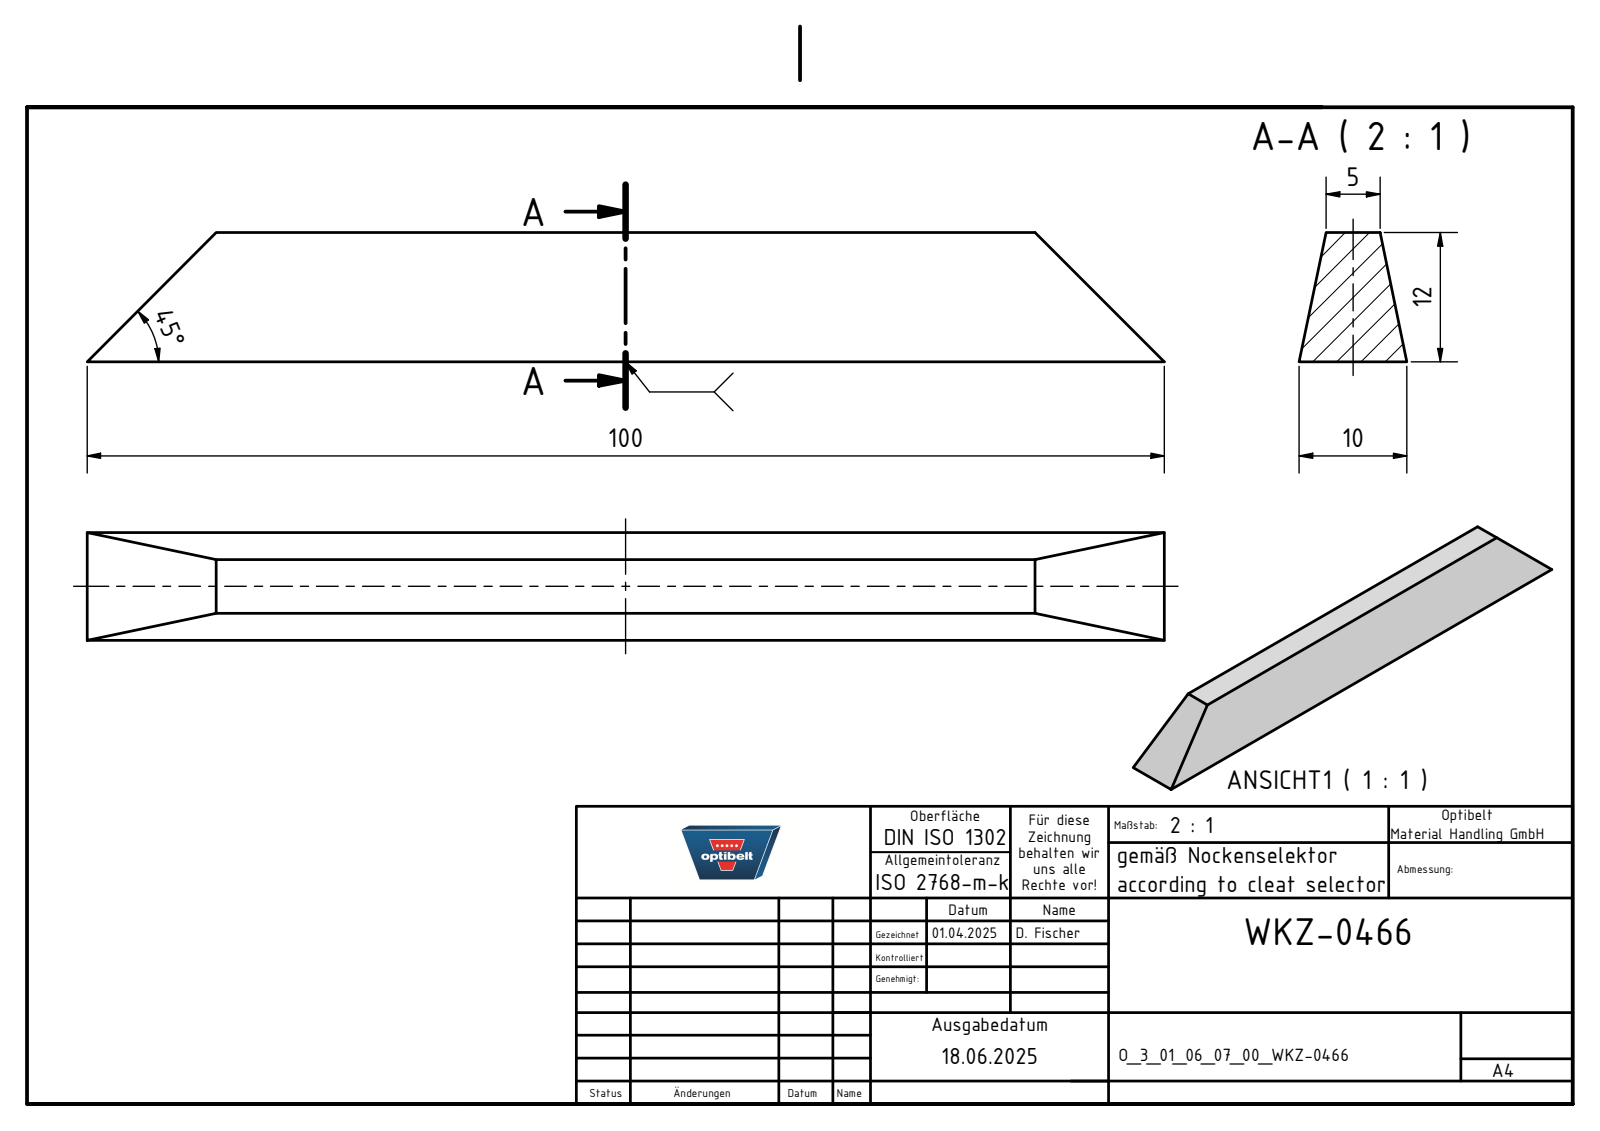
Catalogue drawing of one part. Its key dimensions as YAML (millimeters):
part_name: "O_3_01_06_07_00_WKZ-0466"
step_written_by: "Autodesk Inventor 2025 (AUTOMOTIVE_DESIGN)"
units: millimeters
bodies: {solids: 1, faces: 6, planar: 6, cylindrical: 0, other: 0}
overall_size: [100, 12, 10]
volume: 8040
surface_area: 3792
face_to_face_distances: [12]
